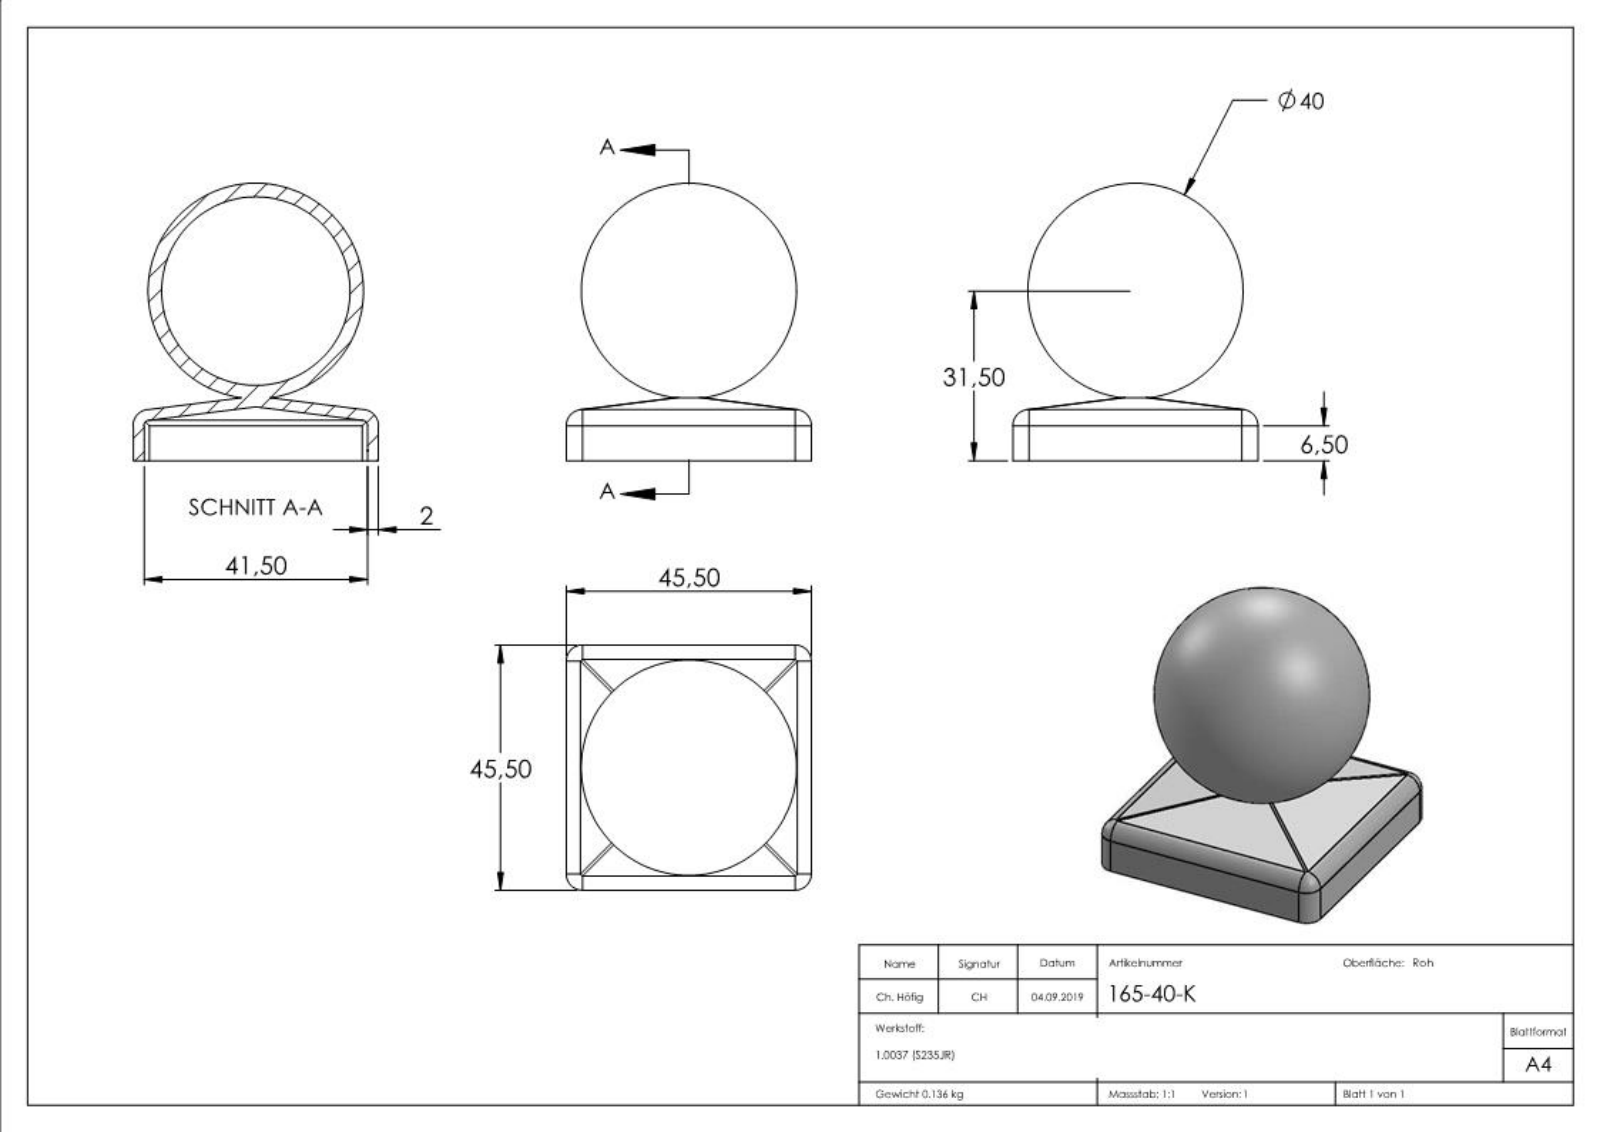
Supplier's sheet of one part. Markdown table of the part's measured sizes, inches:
| quantity | value |
| --- | --- |
| part name | 165-40-K |
| STEP written by | SolidWorks 2015 (CONFIG_CONTROL_DESIGN) |
| units | inches |
| bodies | 1 solid, 334 faces (170 planar, 24 cylindrical, 140 other) |
| overall size | 2.028 × 1.791 × 1.791 |
| volume | 1.066 in³ |
| surface area | 24.18 in² |
| partial cylindrical surfaces (radius × count) | 0.118 × 12, 0.039 × 10 |
| main face-to-face distances | 0.079, 1.713, 1.791, 1.634, 0.075, 1.638, 1.717, 0.826, 0.25, 0.039 |
